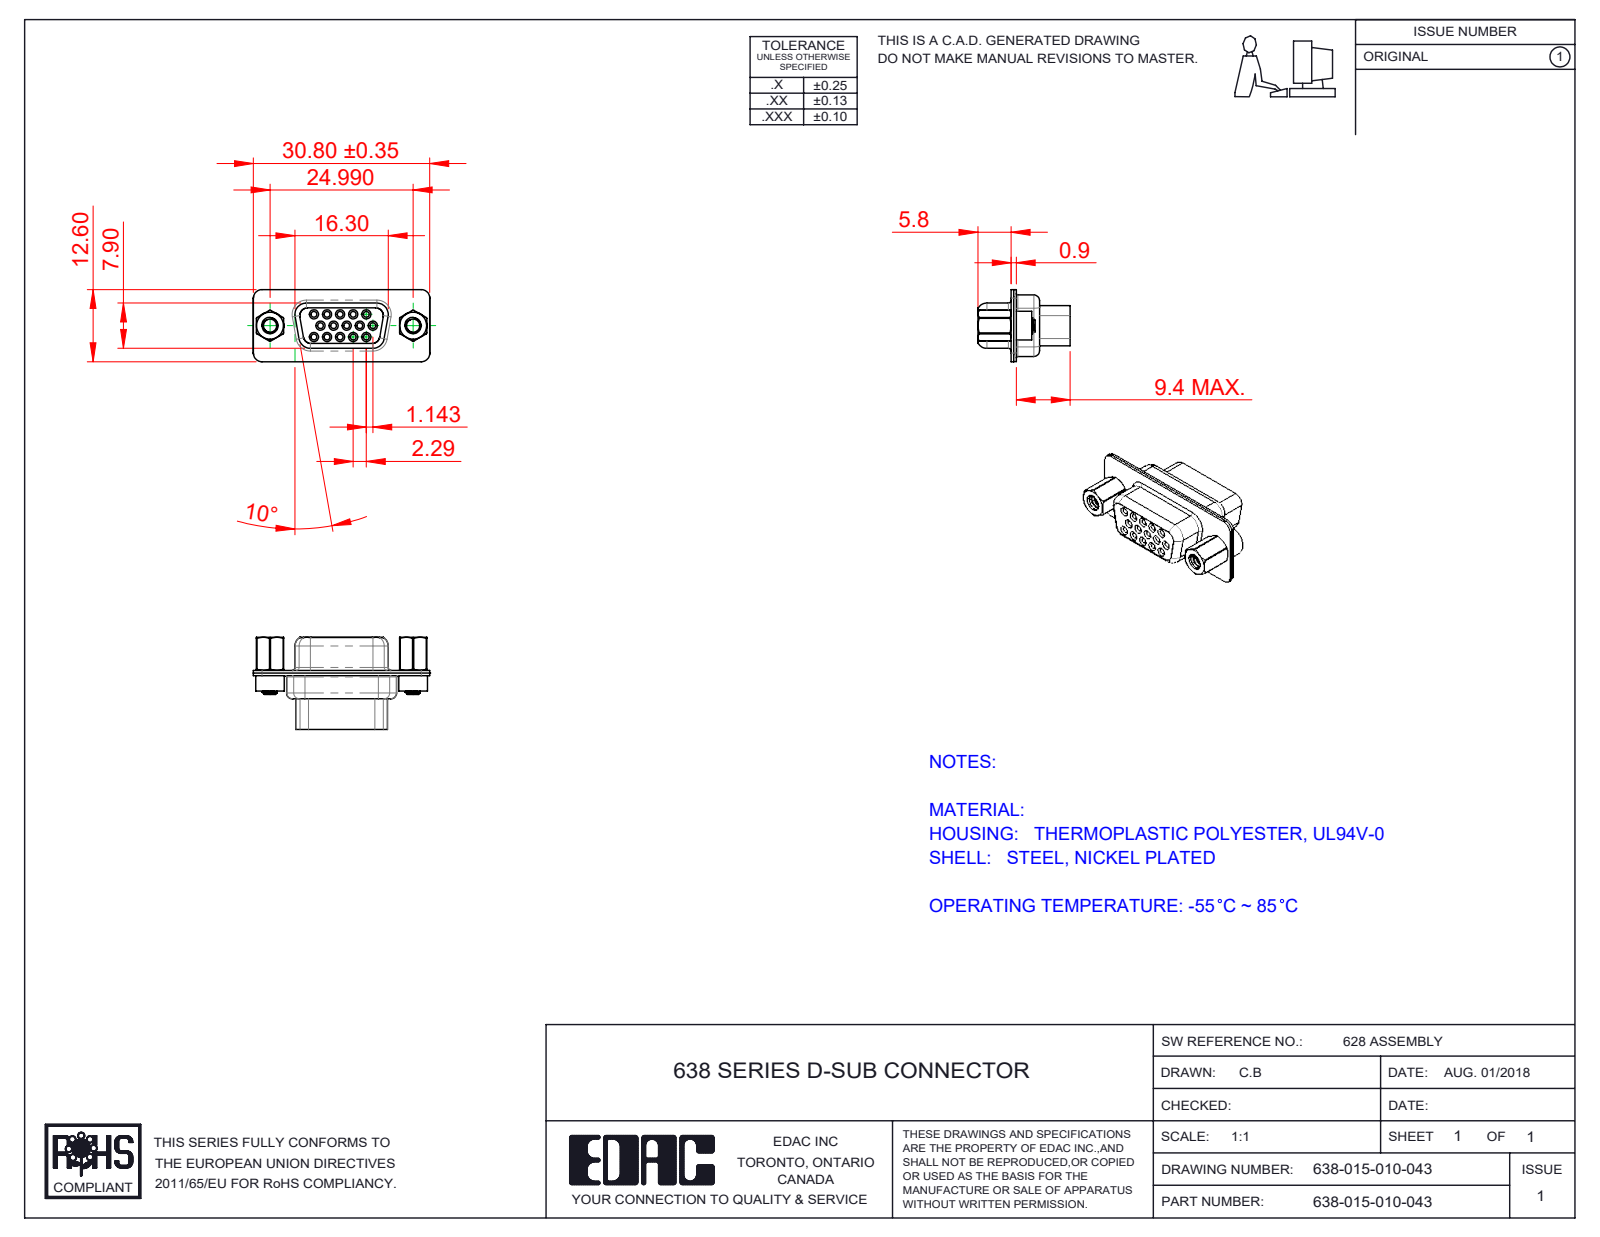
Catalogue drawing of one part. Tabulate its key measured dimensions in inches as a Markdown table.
| quantity | value |
| --- | --- |
| part name | 638-015-010-043; 638 4-40 Hex Standoff; 638 4-40 Threaded Rivet; 638 Housing_15 Contacts HP (+2 more) |
| STEP written by | SolidWorks 2020 (CONFIG_CONTROL_DESIGN) |
| units | inches |
| bodies | 7 solids, 600 faces (134 planar, 329 cylindrical, 137 other) |
| overall size | 1.213 × 0.634 × 0.496 |
| volume | 0.117 in³ |
| surface area | 7.801 in² |
| round holes (diameter × count) | 0.039 × 15, 0.067 × 15, 0.071 × 15, 0.079 × 15, 0.089 × 2, 0.09 × 2, 0.157 × 2, 0.159 × 2, 0.191 × 2 |
| round bosses / shafts (diameter × count) | 0.197 × 2, 0.195 × 2, 0.189 × 2, 0.11 × 2 |
| partial cylindrical surfaces (radius × count) | 0.059 × 20, 0.079 × 12, 0.061 × 8, 0.053 × 5, 0.01 × 4, 0.02 × 4, 0.022 × 4, 0.028 × 4 |
| main face-to-face distances | 0.018, 0.035, 0.016, 0.056, 0.35, 0.26, 0.37, 0.276, 0.264, 0.228 |
| hole center spacings | 0.156, 0.09, 0.18, 0.09, 0.238, 0.27, 0.312, 0.238 |
